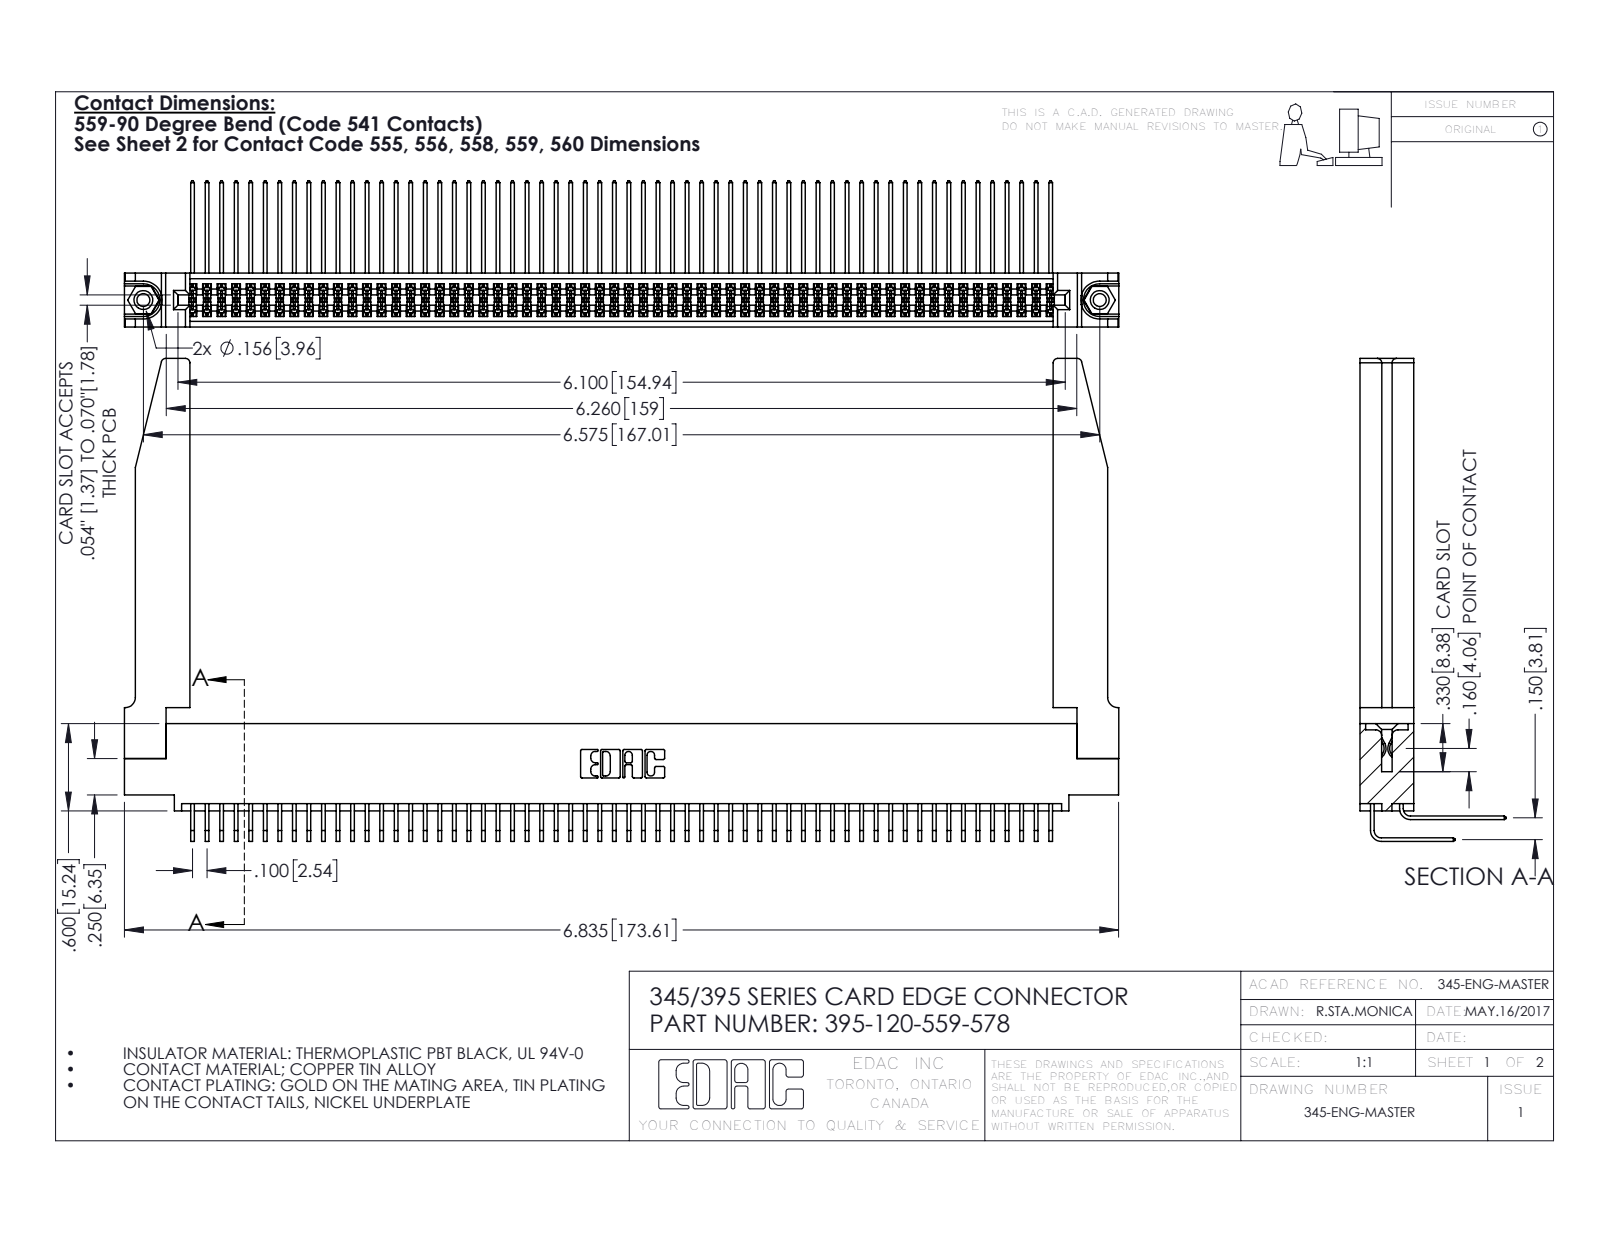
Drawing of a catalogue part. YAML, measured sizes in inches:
part_name: "345 Part_0.110 Offset - 0.156 Dia-TH; 395-120-559-578; 345-250-001_345-250-001-102; 345-220-078_345-220-078 (+2 more)"
step_written_by: "SolidWorks 2016 (CONFIG_CONTROL_DESIGN)"
units: inches
bodies: {solids: 125, faces: 6604, planar: 4426, cylindrical: 2126, other: 52}
overall_size: [6.836, 3.319, 1.005]
volume: 1.551
surface_area: 56.78
round_holes:
  - {diameter: 0.089, count: 2}
  - {diameter: 0.125, count: 2}
  - {diameter: 0.156, count: 2}
  - {diameter: 0.064, count: 1}
round_bosses_or_shafts:
  - {diameter: 0.155, count: 2}
partial_cylinders:
  - {radius: 0.006, count: 181}
  - {radius: 0.01, count: 22}
  - {radius: 0.03, count: 8}
  - {radius: 0.007, count: 6}
  - {radius: 0.031, count: 6}
  - {radius: 0.026, count: 3}
  - {radius: 0.014, count: 2}
  - {radius: 0.019, count: 2}
face_to_face_distances: [0.072, 0.298, 0.37, 0.098, 0.272, 0.025, 0.2, 0.225, 0.175, 0.15]
hole_center_spacings: [0.27, 6.339, 6.575]
